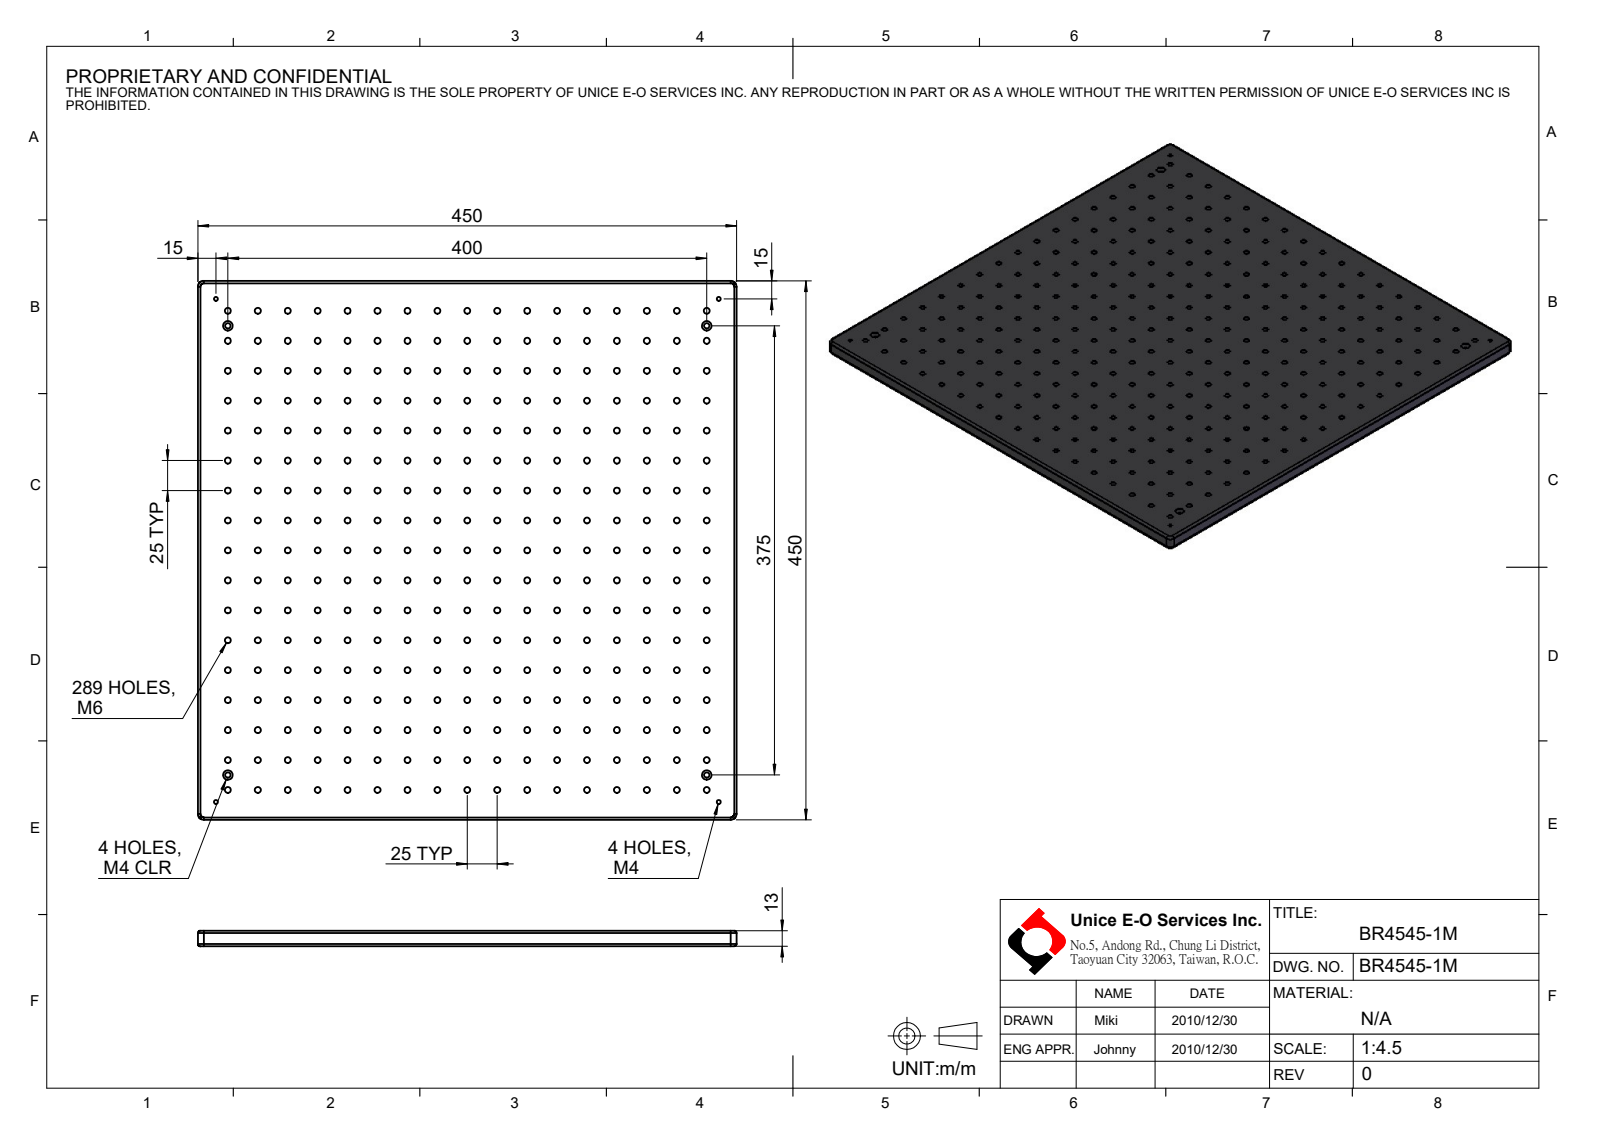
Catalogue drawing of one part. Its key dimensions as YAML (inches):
part_name: "BR4545-1M"
step_written_by: "SolidWorks 2016 (CONFIG_CONTROL_DESIGN)"
units: inches
bodies: {solids: 1, faces: 632, planar: 10, cylindrical: 614, other: 8}
overall_size: [17.717, 17.717, 0.512]
volume: 155.9
surface_area: 734.9
round_holes:
  - {diameter: 0.197, count: 289}
  - {diameter: 0.13, count: 4}
  - {diameter: 0.177, count: 4}
  - {diameter: 0.315, count: 4}
partial_cylinders:
  - {radius: 0.079, count: 8}
  - {radius: 0.197, count: 4}
face_to_face_distances: [0.512, 17.717, 0.339, 0.173]
hole_center_spacings: [0.984, 2.201, 1.392, 1.969, 3.113, 4.058, 2.953, 2.784]
